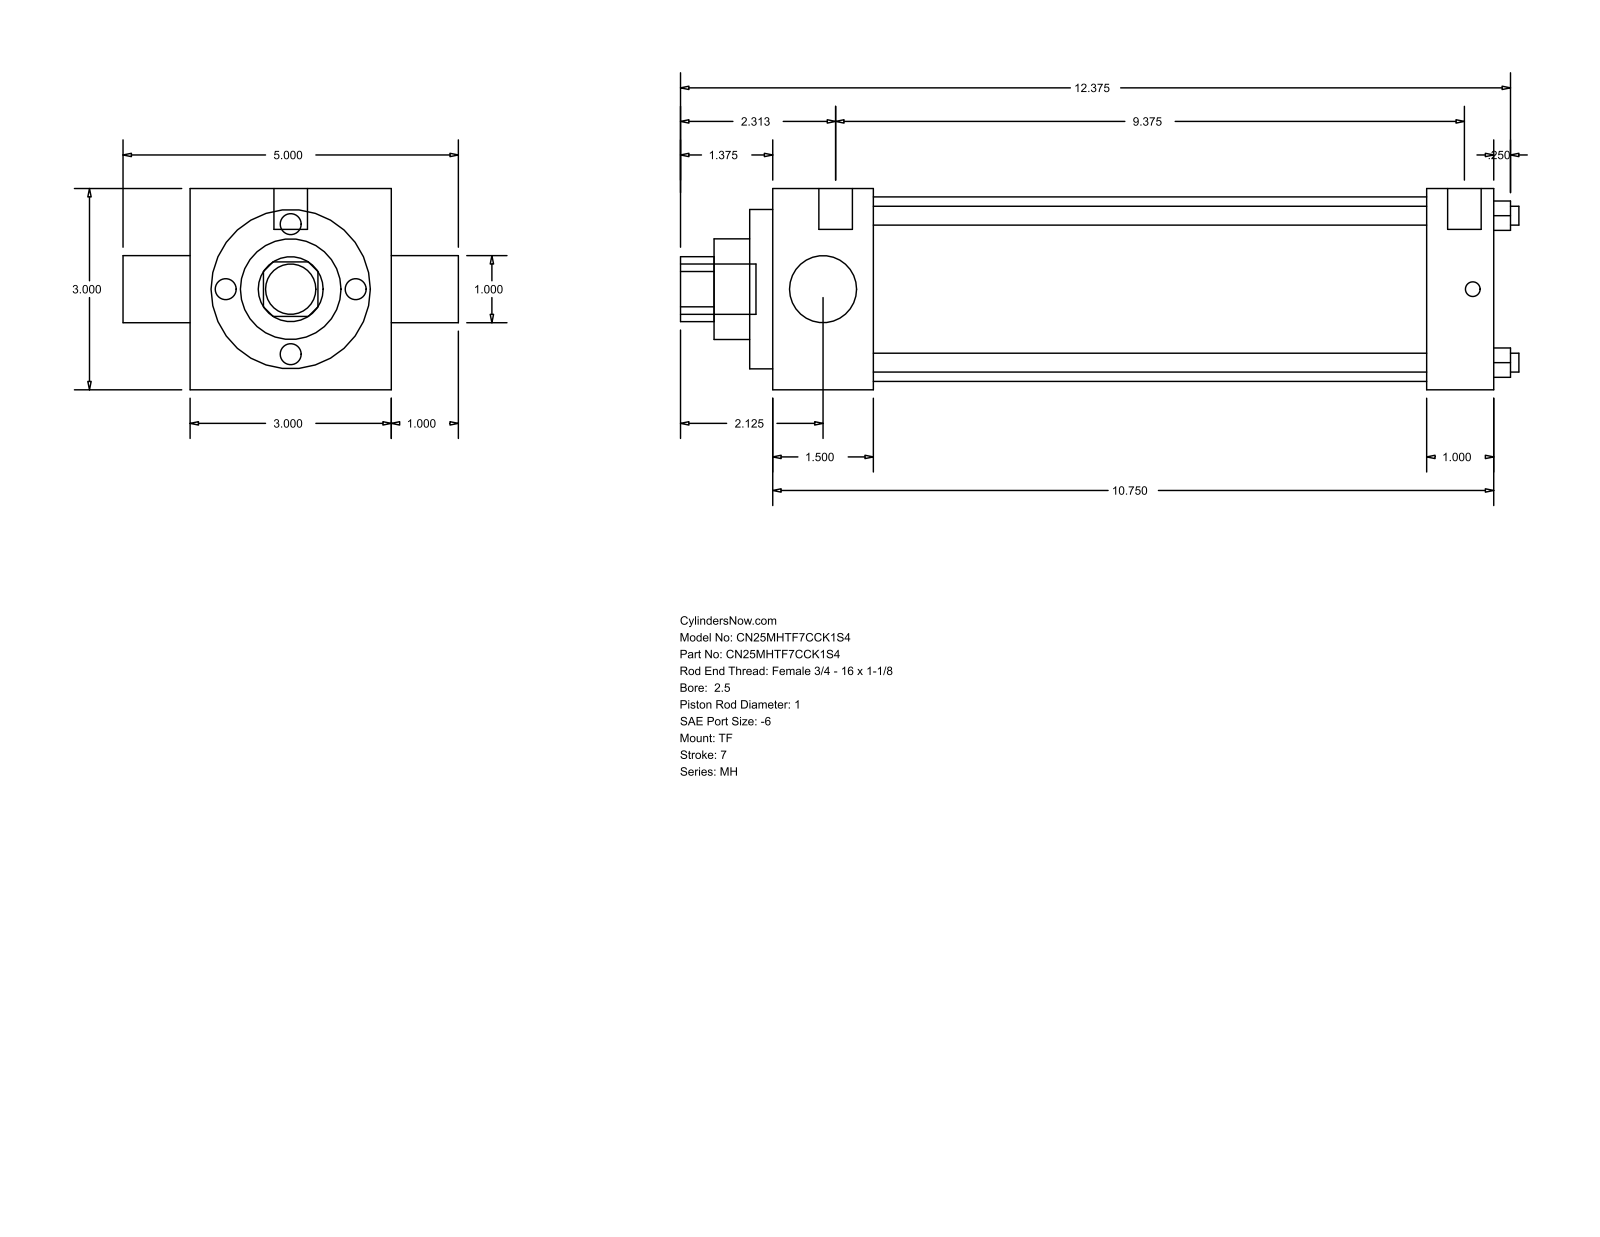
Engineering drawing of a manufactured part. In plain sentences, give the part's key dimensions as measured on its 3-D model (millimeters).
The part is named "MH_TF__0250_1". Its 3-D file was written by "GSSL Pune (CONFIG_CONTROL_DESIGN)". It is 0 solids with 86 faces: 61 planar, 25 cylindrical and 0 other. Overall it measures 317.5 by 127 by 76.2 millimeters. Round holes: 4 of diameter 7.14, 2 of diameter 25.4, 1 of diameter 38.1, 1 of diameter 60.33, 1 of diameter 69.85. Round bosses or shafts: 3 of diameter 5.56, 2 of diameter 12.7, 1 of diameter 19.05. Partial cylindrical surfaces (rounded edges, fillets, slot ends): 1 of radius 12.29. The main face-to-face distances are 76.2, 273.06, 38.11, 234.95, 247.65, 209.54, 25.41, 8.73, 46.84, 256.38. The hole center spacings are 39.33, 55.62, 78.66.
